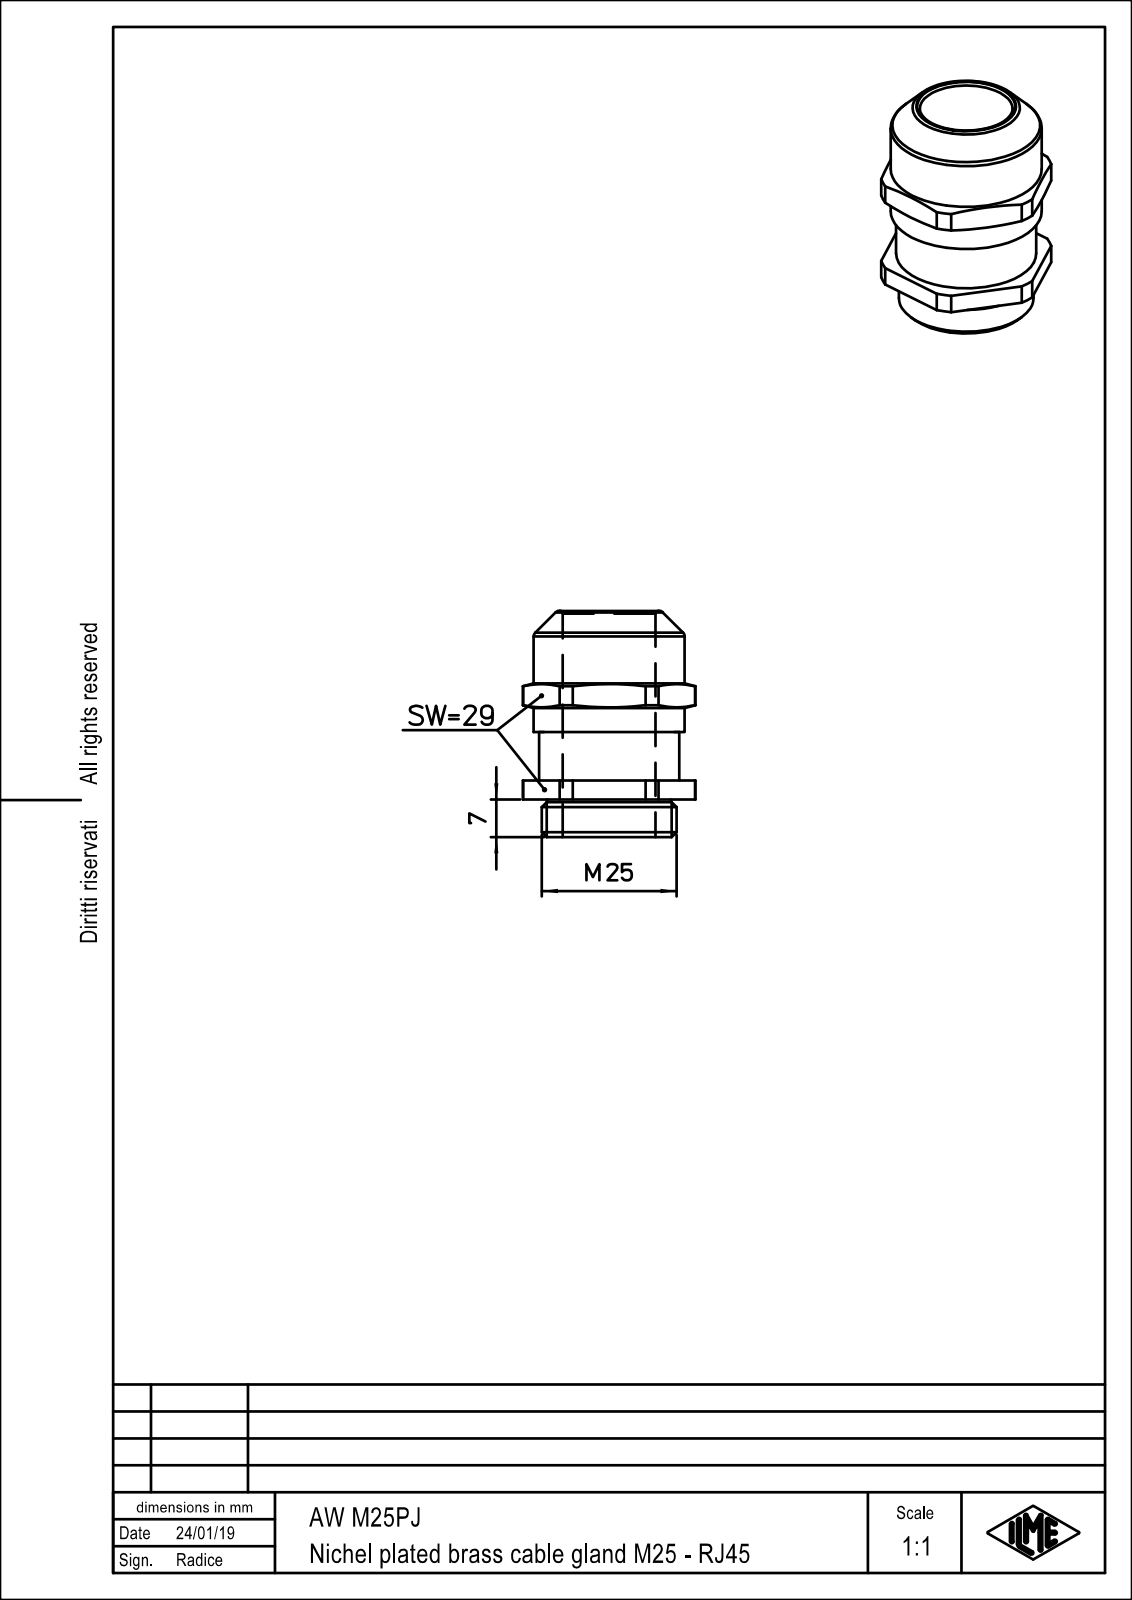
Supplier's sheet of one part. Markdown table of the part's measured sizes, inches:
| quantity | value |
| --- | --- |
| part name | AW_M25PJ |
| STEP written by | PTC Creo Elements/Direct Modeling 19.0E 27-Jun-2016 (C) Parametric Technology GmbH (AUTOMOTIVE_DESIGN) |
| units | inches |
| bodies | 1 solid, 58 faces (18 planar, 24 cylindrical, 16 other) |
| overall size | 1.654 × 1.26 × 1.142 |
| volume | 0.881 in³ |
| surface area | 10.89 in² |
| round holes (diameter × count) | 0.677 × 1 |
| round bosses / shafts (diameter × count) | 1.102 × 1, 1.024 × 1, 0.984 × 1, 0.906 × 1 |
| partial cylindrical surfaces (radius × count) | 0.63 × 1 |
| main face-to-face distances | 1.142, 0.138, 0.276, 0.413, 0.768, 0.492, 0.354, 1.654, 1.378, 1.24 |
